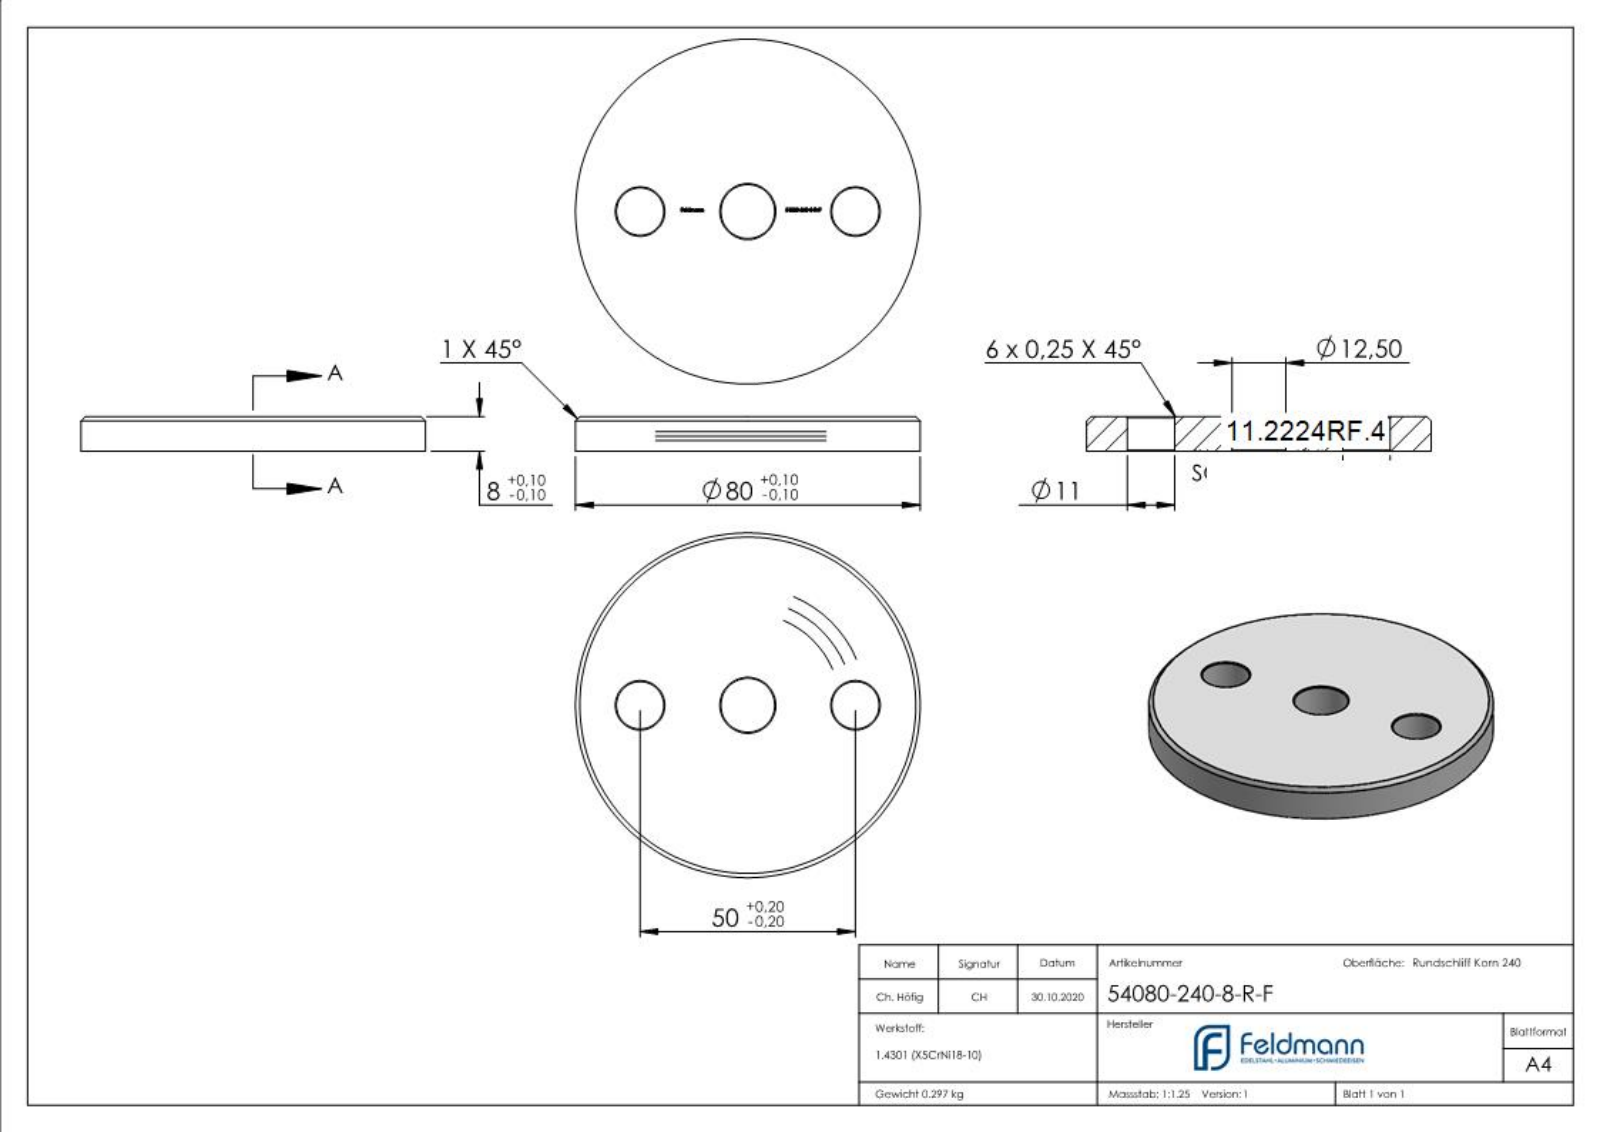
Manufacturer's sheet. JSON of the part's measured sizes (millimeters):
{"part_name": "54080-240-8-R-F", "step_written_by": "SolidWorks 2018 (CONFIG_CONTROL_DESIGN)", "units": "millimeters", "bodies": {"solids": 1, "faces": 317, "planar": 167, "cylindrical": 8, "other": 142}, "overall_size": [80, 80, 8], "volume_mm3": 37578, "surface_area_mm2": 12133, "round_holes": [[11, 2], [12.5, 1]], "round_bosses_or_shafts": [[80, 1]], "face_to_face_distances": [8, 7.9, 0.53, 0.44, 0.35, 2.19, 28.74, 0.32, 28.67, 2.26], "hole_center_spacings": [25, 50]}
